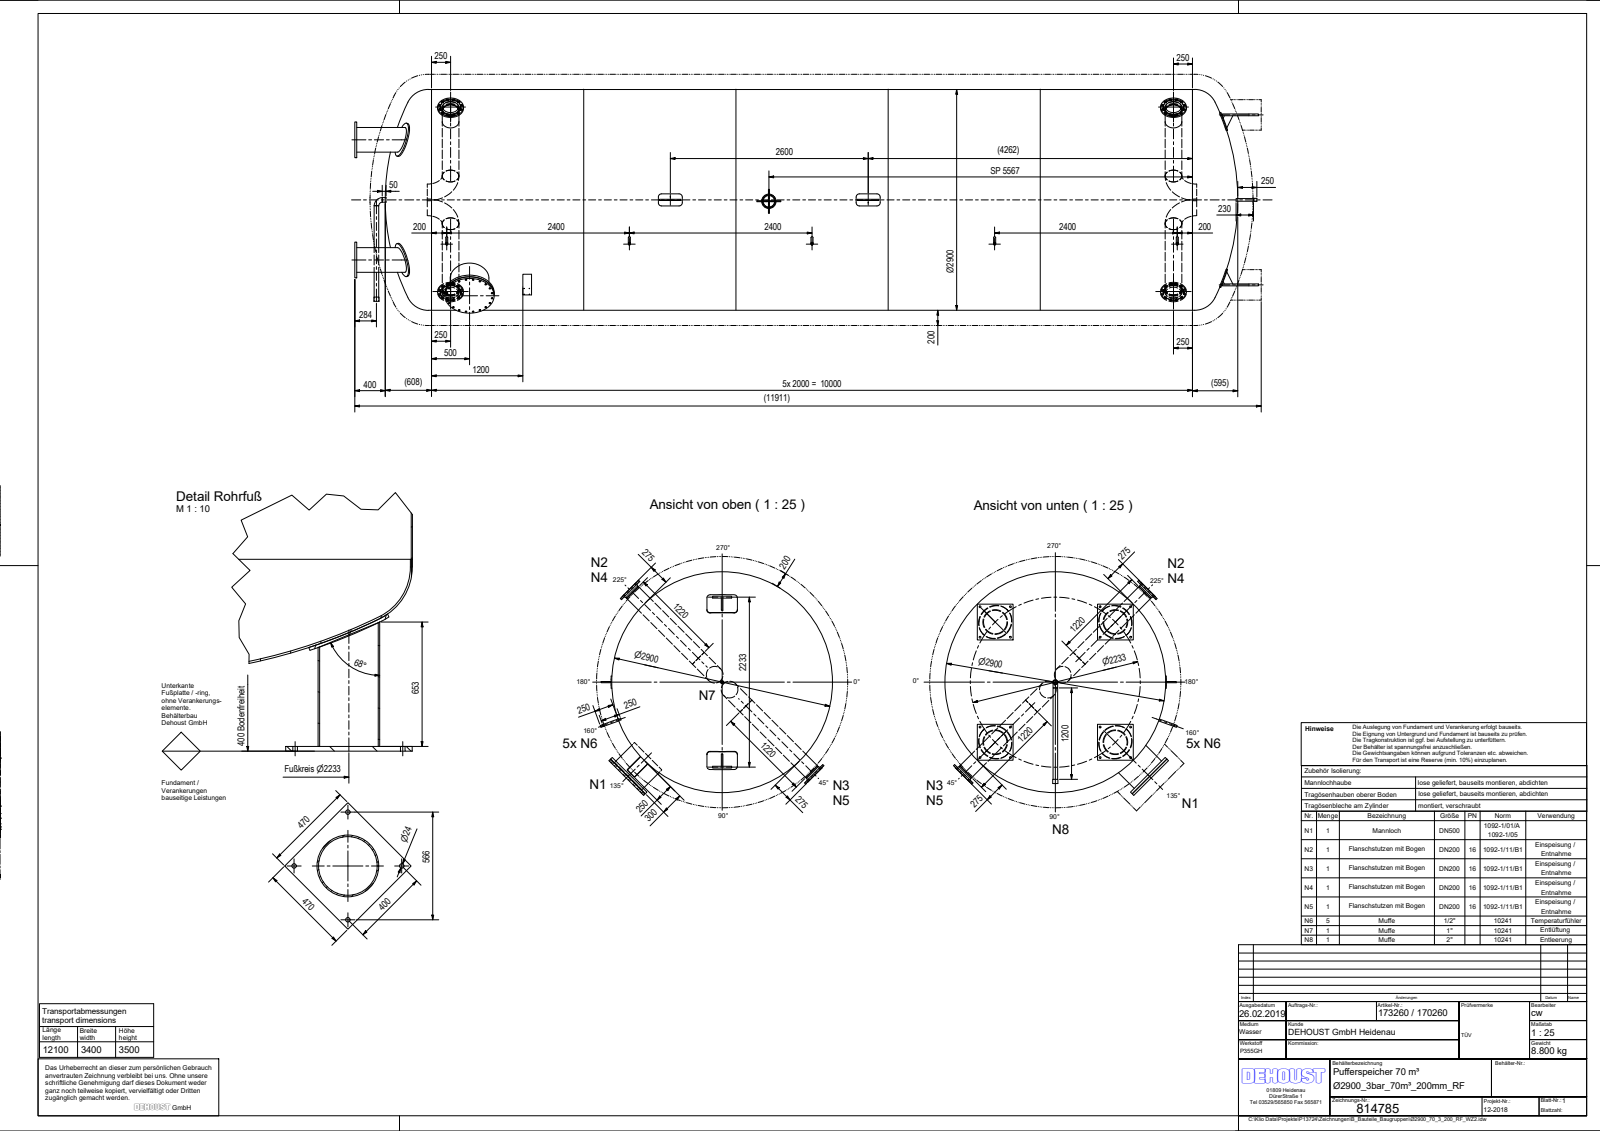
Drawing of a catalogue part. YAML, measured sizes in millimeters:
part_name: "Ø2900_70_3_200_RF_WZ2; Klöpper_Gew_Ø2900_7,5; Klöpper_Gew_Ø2900_10,3; Zyl_Ø2900_6x10000_2019 (+8 more)"
step_written_by: "Autodesk Inventor 2019 (AUTOMOTIVE_DESIGN)"
units: millimeters
bodies: {solids: 58, faces: 465, planar: 178, cylindrical: 241, other: 46}
overall_size: [11874.42, 3051.99, 2937.4]
volume: 1042000000
surface_area: 240700000
round_holes:
  - {diameter: 22, count: 80}
  - {diameter: 24, count: 16}
  - {diameter: 18.63, count: 5}
  - {diameter: 21.7, count: 5}
  - {diameter: 26.9, count: 5}
  - {diameter: 5.8, count: 4}
  - {diameter: 204.9, count: 4}
  - {diameter: 207.3, count: 4}
  - {diameter: 219.1, count: 4}
  - {diameter: 307.9, count: 4}
  - {diameter: 5, count: 2}
  - {diameter: 52.3, count: 2}
round_bosses_or_shafts:
  - {diameter: 219.1, count: 8}
  - {diameter: 26.9, count: 5}
  - {diameter: 26.4, count: 5}
  - {diameter: 450, count: 4}
  - {diameter: 340, count: 4}
  - {diameter: 323.9, count: 4}
  - {diameter: 268, count: 4}
  - {diameter: 2900, count: 1}
partial_cylinders:
  - {radius: 42, count: 16}
  - {radius: 10, count: 6}
  - {radius: 6, count: 4}
  - {radius: 5, count: 2}
  - {radius: 36, count: 2}
  - {radius: 72, count: 2}
  - {radius: 125, count: 1}
  - {radius: 1460, count: 1}
face_to_face_distances: [25, 600, 5687.96, 6327.96, 5662.96, 6302.96, 640, 27.99, 4680, 5320]
hole_center_spacings: [300, 147.5, 185.41, 93.86, 2400, 352.67, 592.61, 4800]
